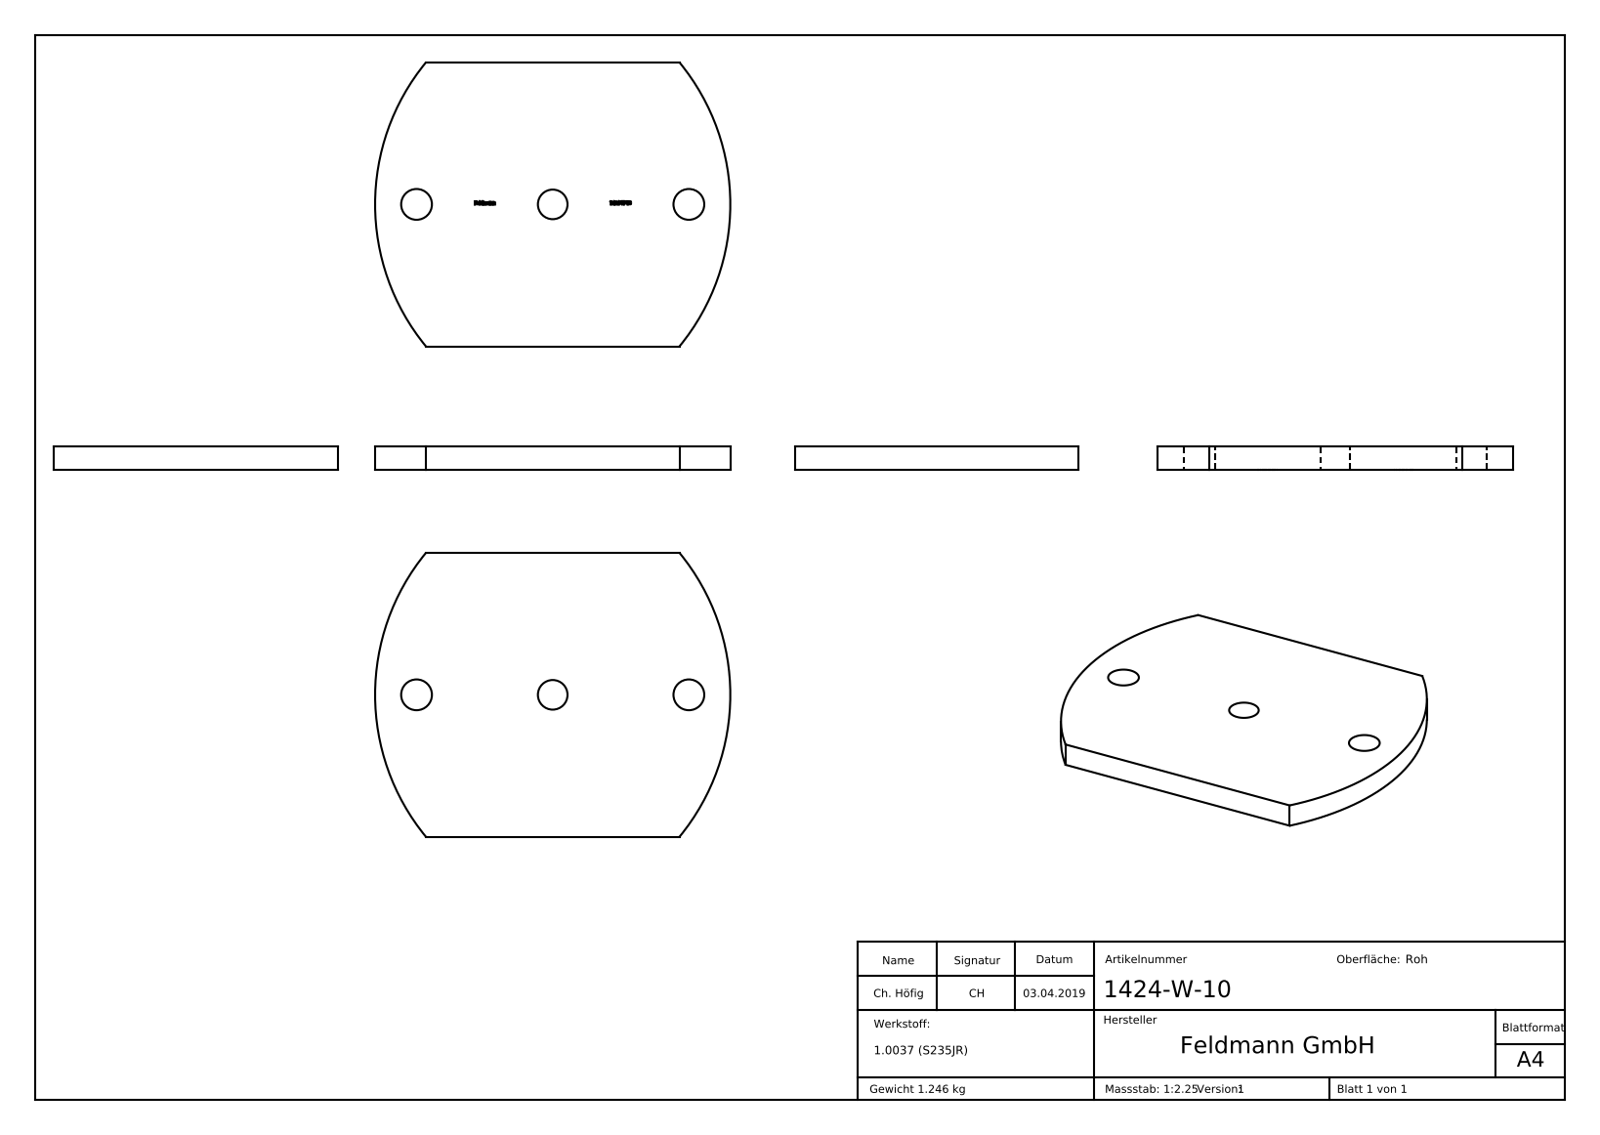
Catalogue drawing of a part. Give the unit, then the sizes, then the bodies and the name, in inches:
Units: inches
Overall size (bounding box): 5.906 × 4.724 × 0.394
Round holes (diameter × count): ⌀0.512 ×2, ⌀0.492 ×1
Partial cylindrical surfaces — rounded edges, fillets, slot ends (radius × count): R3.719 ×2
Main face-to-face distances: 0.394, 4.724, 0.39, 0.08, 0.021, 2.184, 2.462, 0.278, 0.044, 2.317
Hole centre spacings: 2.264, 4.528
Volume: 9.751 in³ · Surface area: 58.77 in²
Bodies: 1 solid, 217 faces (146 planar, 8 cylindrical, 63 other)
Part name (STEP PRODUCT): 1424-W-10
STEP written by: SolidWorks 2015 (CONFIG_CONTROL_DESIGN)
